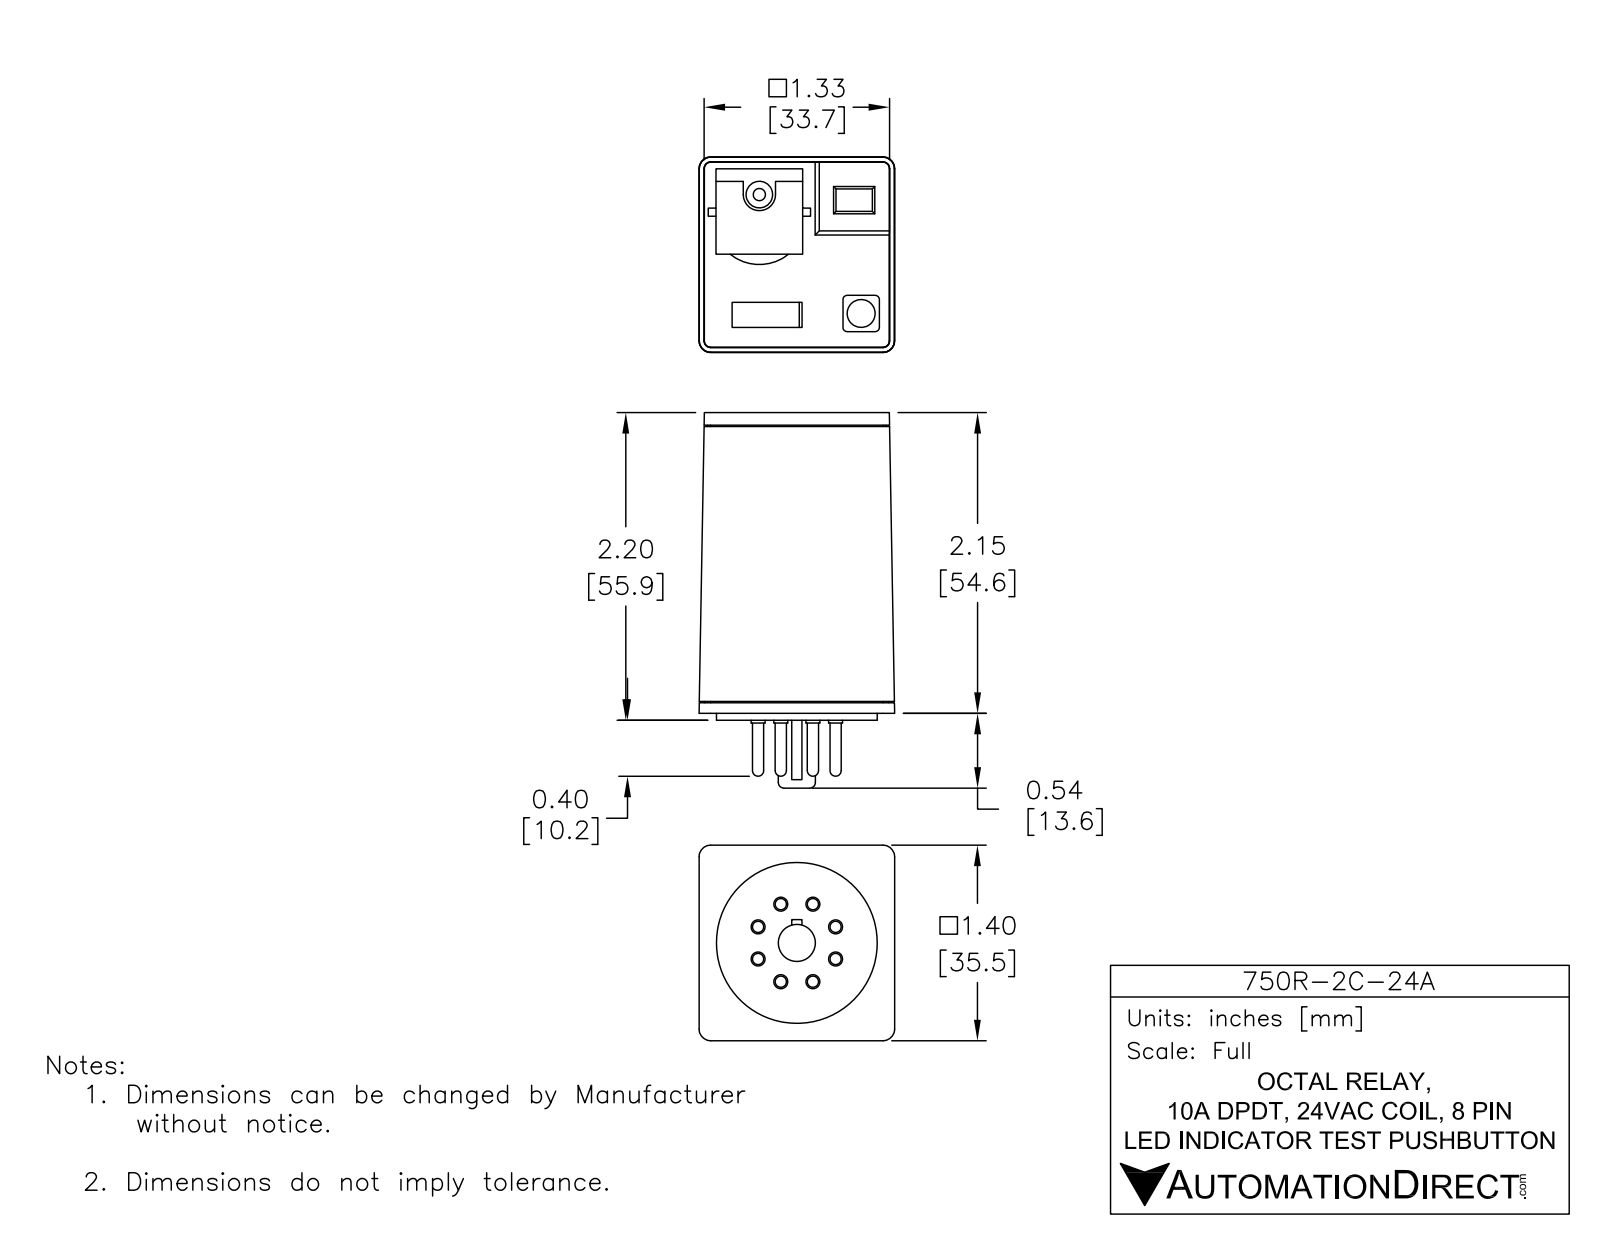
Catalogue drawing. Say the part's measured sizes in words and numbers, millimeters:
The part is named "750R-2C-24A". Its 3-D file was written by "SolidWorks 2014 (AUTOMOTIVE_DESIGN)". It is 1 solid with 162 faces: 90 planar, 50 cylindrical and 22 other. Overall it measures 68.2 by 35.5 by 35.5 millimeters. Its volume is 66 320 cubic millimeters and its surface area 11 210 square millimeters. Round holes: 1 of diameter 2.2, 1 of diameter 5.1. Round bosses or shafts: 8 of diameter 2.5, 8 of diameter 2, 1 of diameter 29.2, 1 of diameter 6.7, 1 of diameter 4.8. Partial cylindrical surfaces (rounded edges, fillets, slot ends): 4 of radius 0.8, 1 of radius 2.9, 1 of radius 8.4. The main face-to-face distances are 1.3, 54.6, 55.9, 53.6, 1, 55.6, 54.4, 2.2, 0.8, 54.9. The hole center spacings are 28.4.
